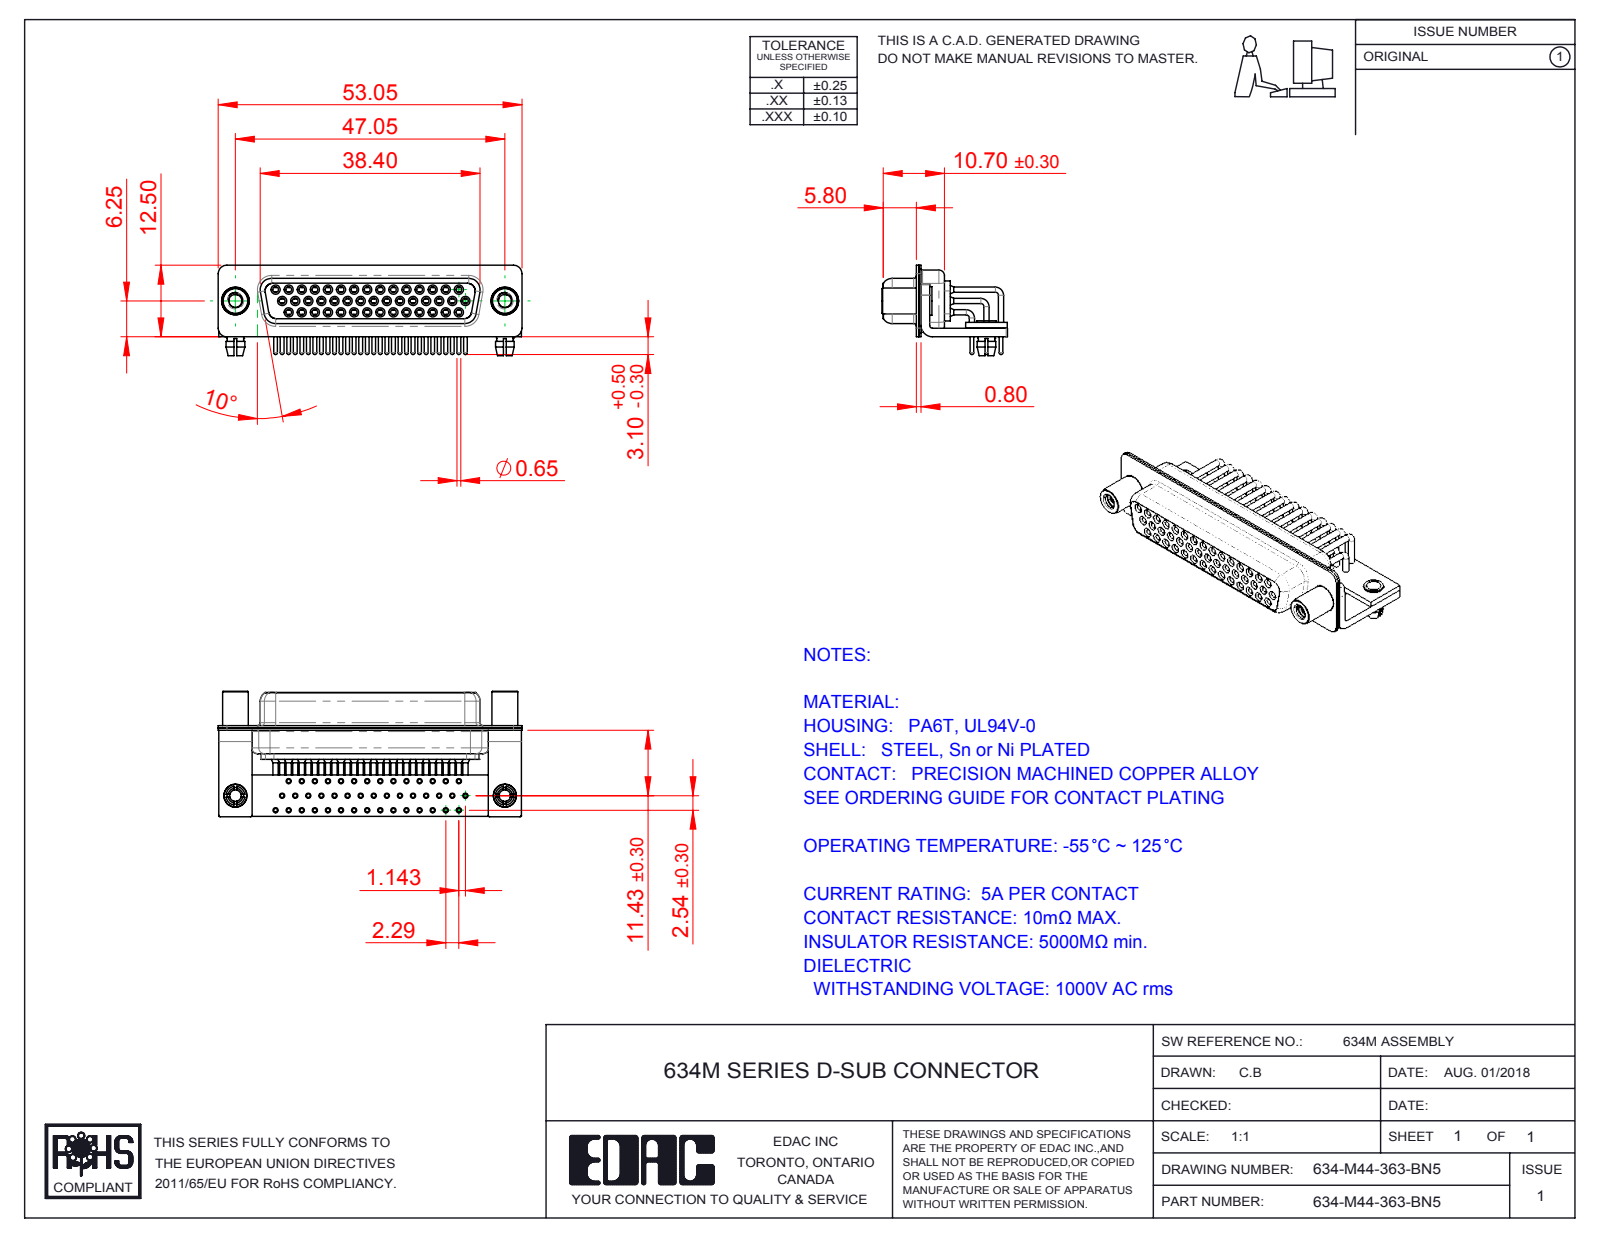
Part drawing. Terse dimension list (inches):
name: 634M Stabilizer Bracket; 634M Shell Front_44 Contacts; 634M 4-40 Threaded Standoff; 634M Stabilizer Board_44 Contacts (+7 more)
written by: SolidWorks 2016 (CONFIG_CONTROL_DESIGN)
unit: in
bodies: 54 solids, 2891 faces (803 planar, 1333 cylindrical, 755 other)
size: 2.089 × 0.862 × 0.622
volume: 0.283 in³; area: 23.49 in²
holes: 46× ⌀0.079, 44× ⌀0.035, 44× ⌀0.039, 44× ⌀0.043, 44× ⌀0.067, 44× ⌀0.071, 2× ⌀0.089, 2× ⌀0.098, 2× ⌀0.126, 2× ⌀0.157, 2× ⌀0.189
bosses: 44× ⌀0.063, 44× ⌀0.059, 44× ⌀0.035, 44× ⌀0.026, 2× ⌀0.197, 2× ⌀0.193, 2× ⌀0.177, 2× ⌀0.157
rounds: 16× R0.01, 16× R0.059, 13× R0.079, 8× R0.053, 8× R0.063, 5× R0.02, 4× R0.024, 4× R0.026
face distances: 0.016, 0.091, 0.075, 0.039, 0.031, 0.368, 0.335, 0.059, 0.057, 0.352
hole spacings: 0.09, 0.09, 0.18, 0.27, 0.45, 0.156, 0.324, 0.36
